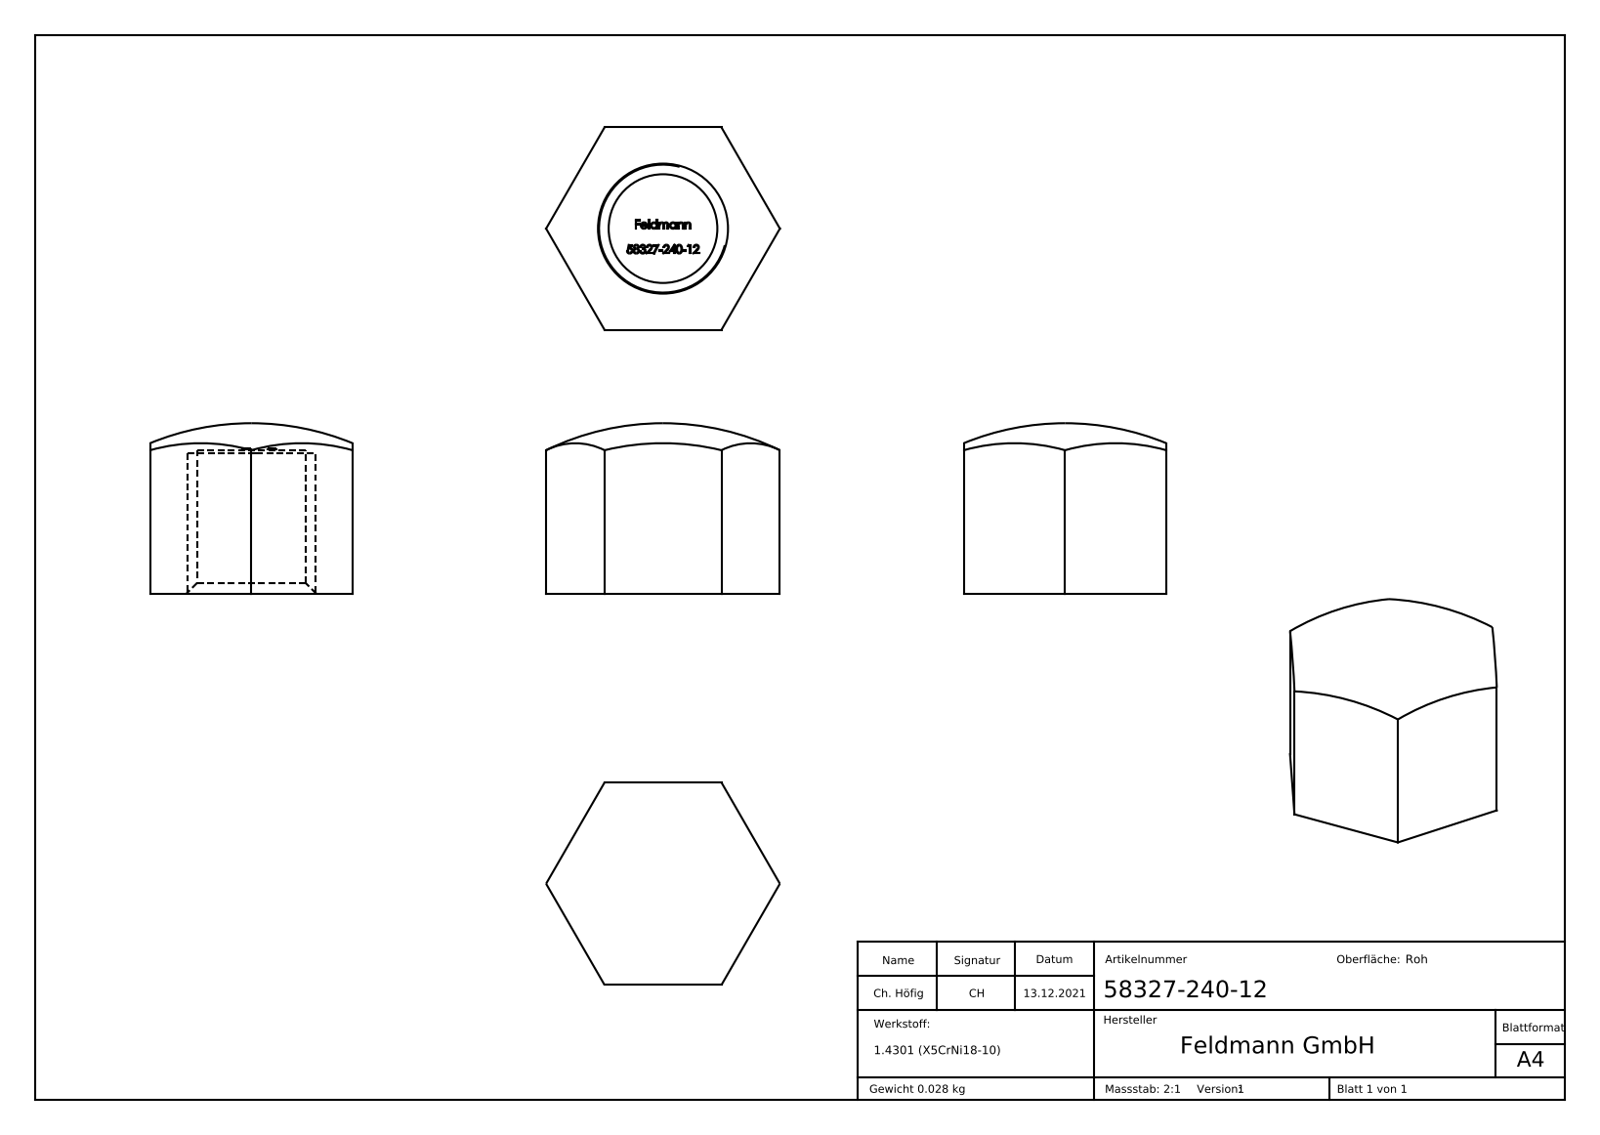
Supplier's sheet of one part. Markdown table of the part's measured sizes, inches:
| quantity | value |
| --- | --- |
| part name | 58327-240-12 |
| STEP written by | SolidWorks 2018 (CONFIG_CONTROL_DESIGN) |
| units | inches |
| bodies | 1 solid, 266 faces (149 planar, 1 cylindrical, 116 other) |
| overall size | 0.864 × 0.748 × 0.63 |
| volume | 0.217 in³ |
| surface area | 3.063 in² |
| round holes (diameter × count) | 0.402 × 1 |
| main face-to-face distances | 0.748, 0.531, 0.535, 0.096, 0.039, 0.042, 0.07, 0.015, 0.028, 0.033 |
